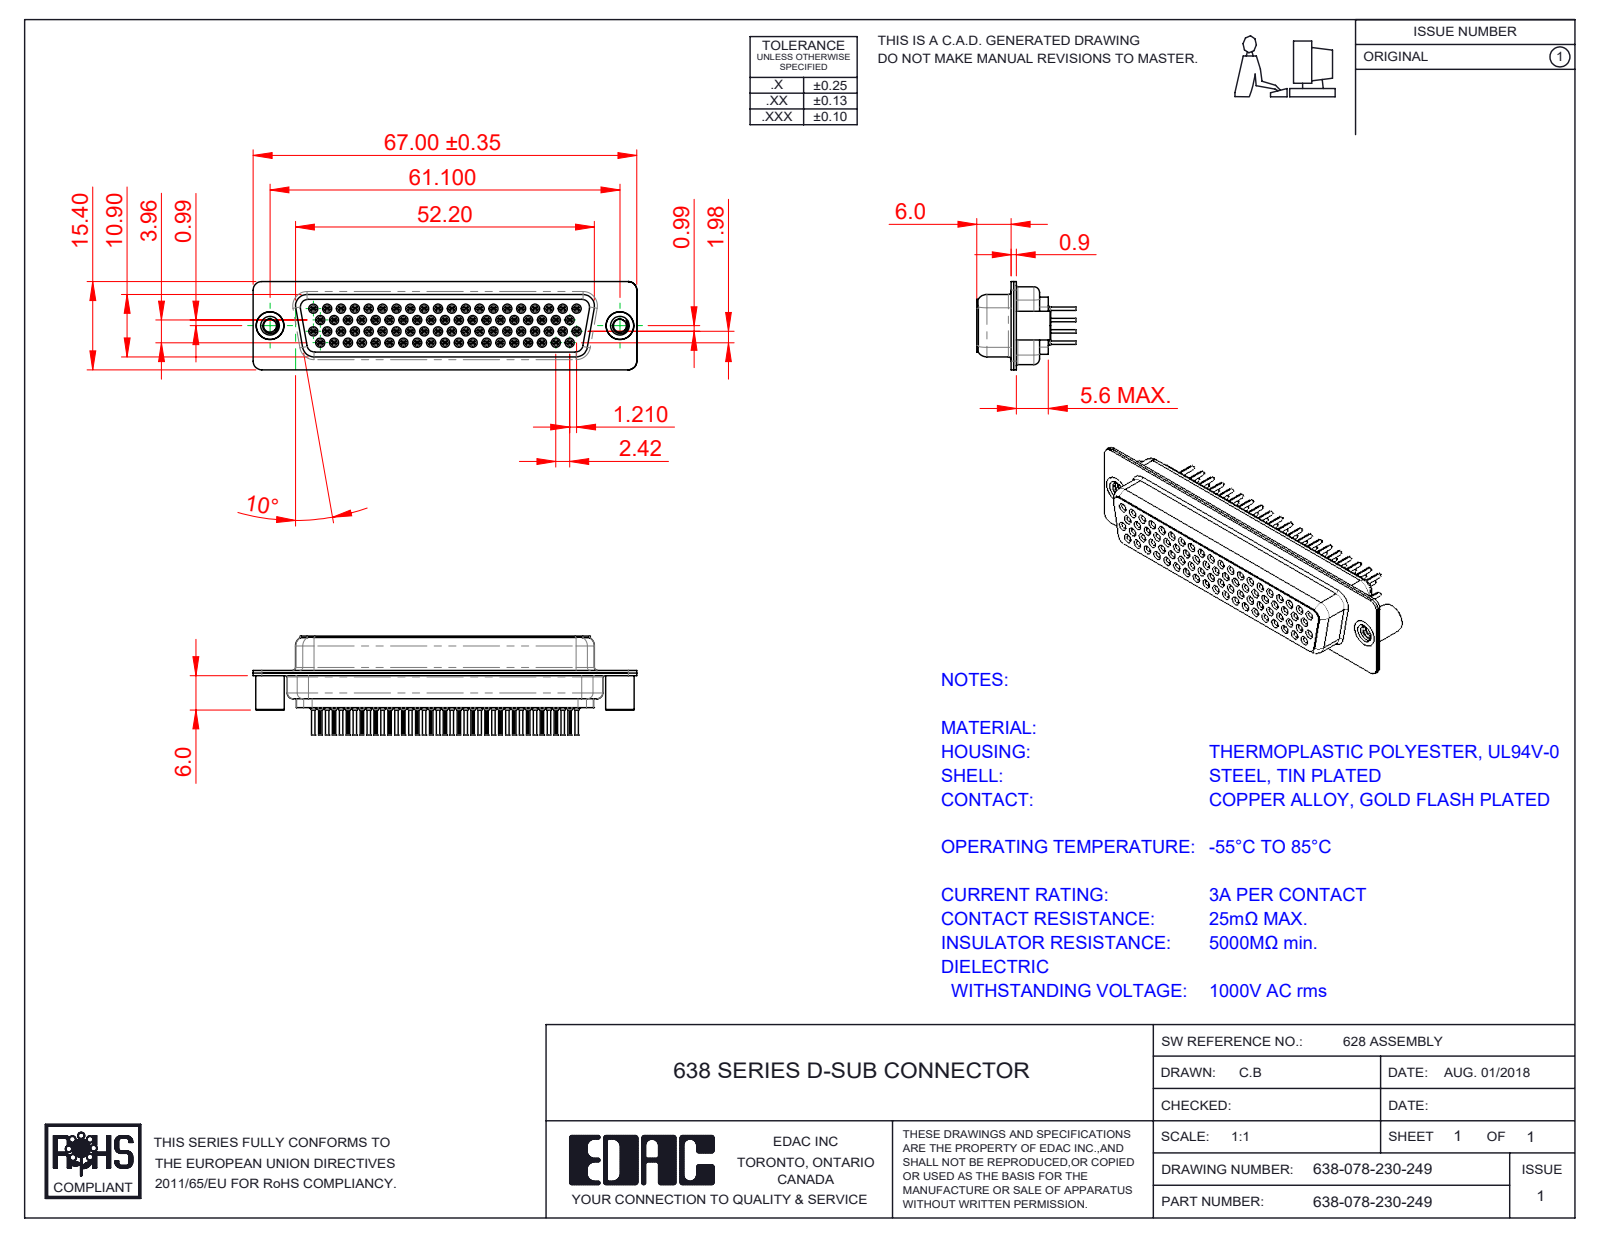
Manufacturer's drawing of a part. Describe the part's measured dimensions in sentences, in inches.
The part is named "638 Contact Row 78_30; 638 Shell Front_78 Contacts; 638 Contact Row 3_30; 638 Shell Rear_78 Contacts (+5 more)". Its 3-D file was written by "SolidWorks 2020 (CONFIG_CONTROL_DESIGN)". It is 83 solids with 10207 faces: 2485 planar, 2731 cylindrical and 4991 other. Overall it measures 2.638 by 0.681 by 0.606 inches. Its volume is 0.364 cubic inches and its surface area 32.11 square inches. Round holes: 78 of diameter 0.008, 78 of diameter 0.031, 78 of diameter 0.039, 78 of diameter 0.043, 78 of diameter 0.063, 78 of diameter 0.067, 78 of diameter 0.071, 2 of diameter 0.089, 2 of diameter 0.157, 2 of diameter 0.159, 2 of diameter 0.191. Round bosses or shafts: 78 of diameter 0.079, 78 of diameter 0.059, 78 of diameter 0.047, 78 of diameter 0.024, 2 of diameter 0.197, 2 of diameter 0.195, 2 of diameter 0.189, 1 of diameter 0.157. Partial cylindrical surfaces (rounded edges, fillets, slot ends): 156 of radius 0.004, 39 of radius 0.011, 16 of radius 0.059, 12 of radius 0.079, 8 of radius 0.061, 4 of radius 0.01, 4 of radius 0.02, 4 of radius 0.022. The main face-to-face distances are 0.018, 0.016, 0.035, 0.053, 0.378, 0.465, 0.071, 0.449, 0.087, 0.518. The hole center spacings are 0.095, 0.191, 0.286, 0.381, 0.239, 0.476, 0.274, 0.334.
